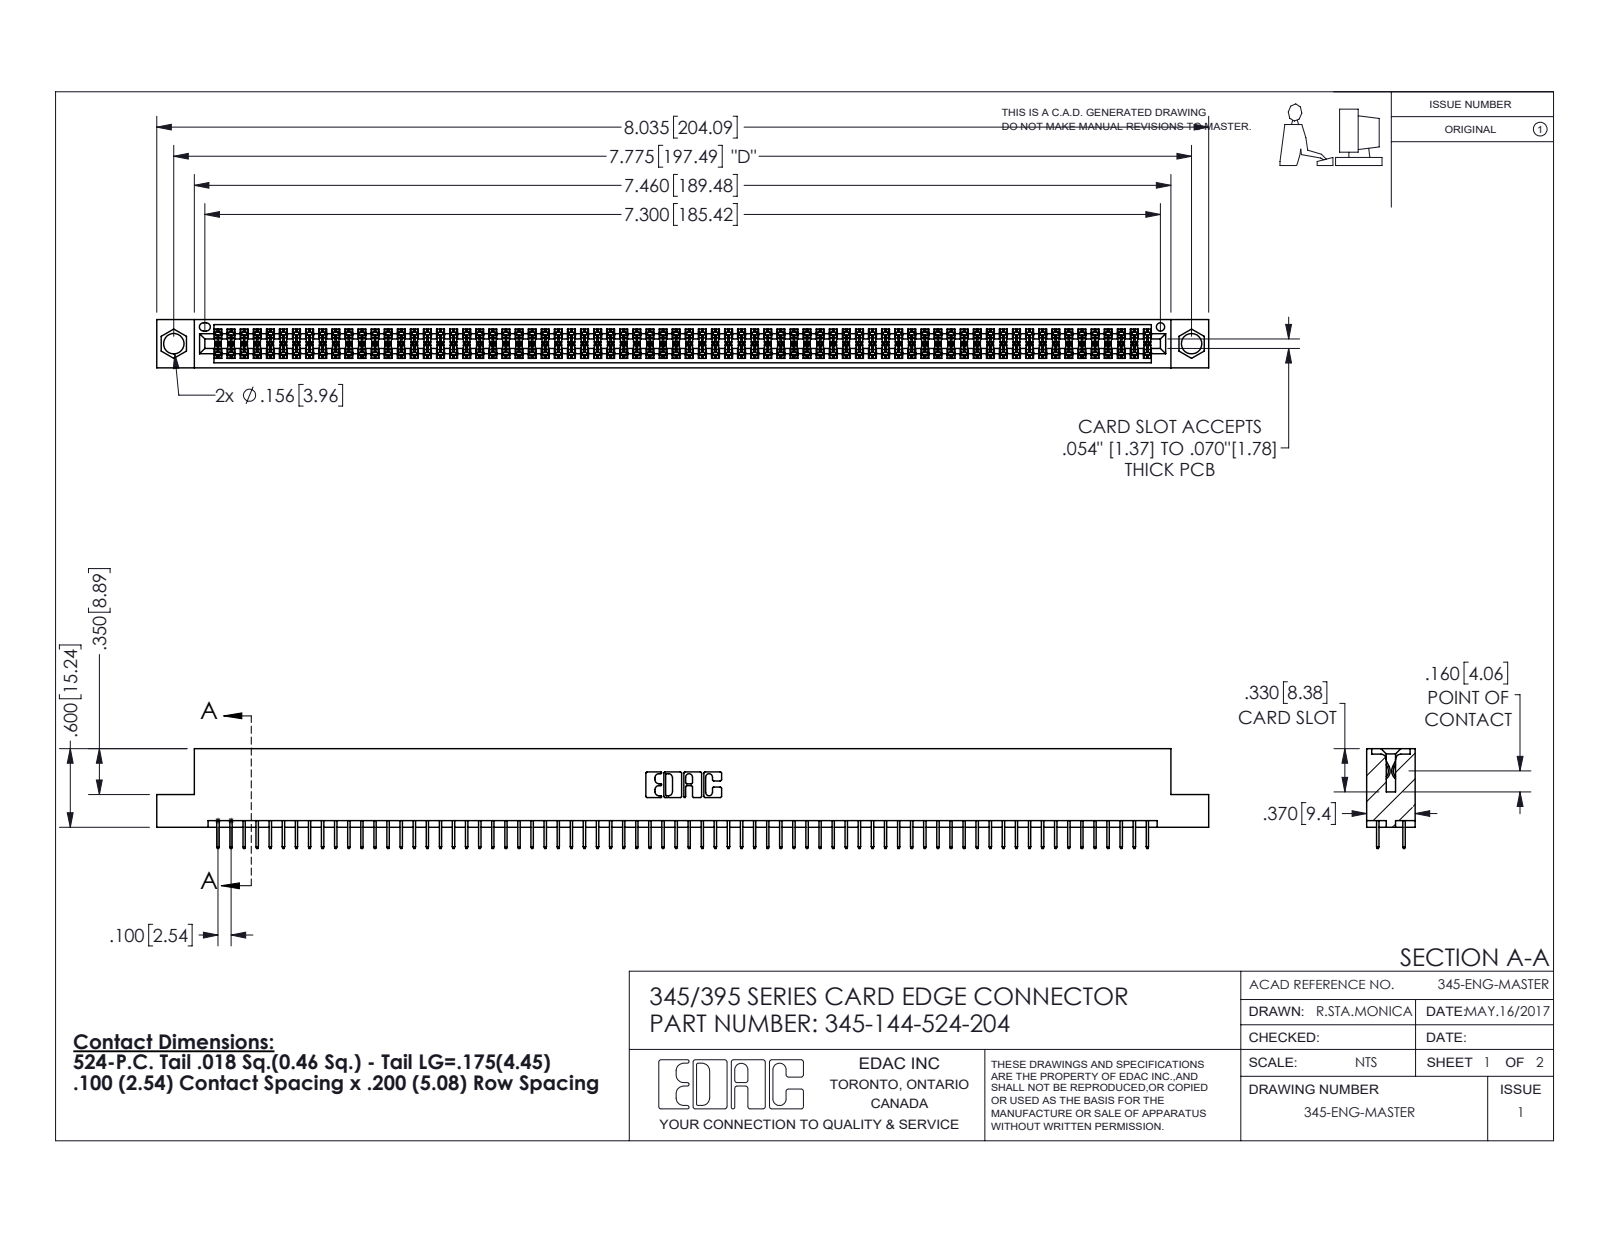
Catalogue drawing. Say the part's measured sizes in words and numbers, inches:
The part is named "345-144-524-204; 345 Part_Flush Mounting Lugs - 0.156 Dia-TI; 345-292-001_345-293-124". Its 3-D file was written by "SolidWorks 2020 (CONFIG_CONTROL_DESIGN)". It is 145 solids with 7916 faces: 5710 planar, 2206 cylindrical and 0 other. Overall it measures 8.035 by 0.762 by 0.37 inches. Its volume is 1.207 cubic inches and its surface area 45.1 square inches. Round holes: 2 of diameter 0.156, 1 of diameter 0.064. Partial cylindrical surfaces (rounded edges, fillets, slot ends): 288 of radius 0.006, 22 of radius 0.01, 6 of radius 0.007, 6 of radius 0.031, 3 of radius 0.026, 2 of radius 0.014, 2 of radius 0.019, 2 of radius 0.022. The main face-to-face distances are 0.072, 0.298, 0.2, 0.37, 0.098, 0.272, 0.025, 0.225, 0.072, 0.175. The hole center spacings are 0.27, 7.539, 7.775.
